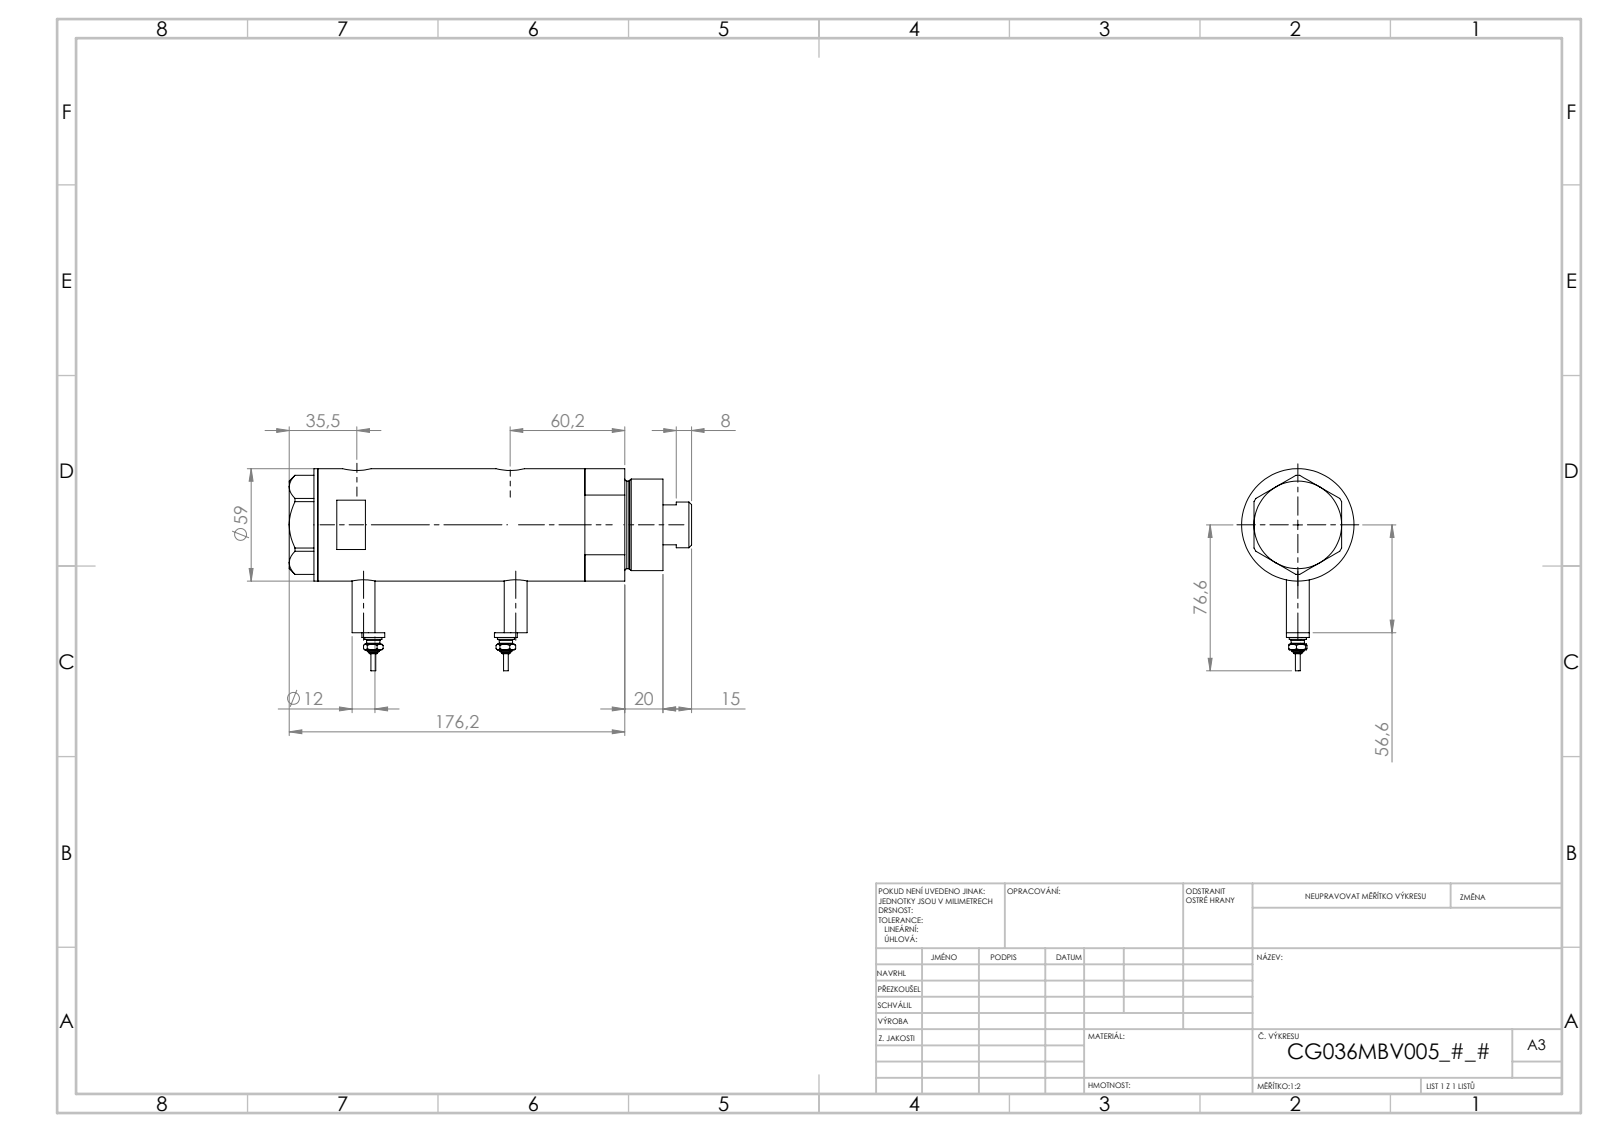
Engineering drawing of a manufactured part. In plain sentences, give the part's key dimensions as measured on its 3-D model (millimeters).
The part is named "V270CG_BACK; V270CG_VC; V270CG_FRONT; V270CG_MIDDLE (+1 more)". Its 3-D file was written by "SolidWorks 2019 (CONFIG_CONTROL_DESIGN)". It is 6 solids with 232 faces: 81 planar, 77 cylindrical and 74 other. Overall it measures 168.42 by 91.3 by 59 millimeters. Its volume is 385 033 cubic millimeters and its surface area 85 725 square millimeters. Round holes: 2 of diameter 5, 2 of diameter 9.73, 2 of diameter 12.5, 2 of diameter 15, 1 of diameter 8.5, 1 of diameter 25, 1 of diameter 26.5, 1 of diameter 36, 1 of diameter 40, 1 of diameter 52. Round bosses or shafts: 3 of diameter 12, 2 of diameter 9, 2 of diameter 7, 2 of diameter 4.34, 2 of diameter 2.4, 1 of diameter 59, 1 of diameter 48, 1 of diameter 46. The main face-to-face distances are 62.34, 23.5, 38.84, 15, 38.5, 77.34, 153.42, 138.42, 114.92, 76.08. The hole center spacings are 2.9, 3.5, 37.15, 40.05, 40.65, 43.55, 2.89, 2.91.
